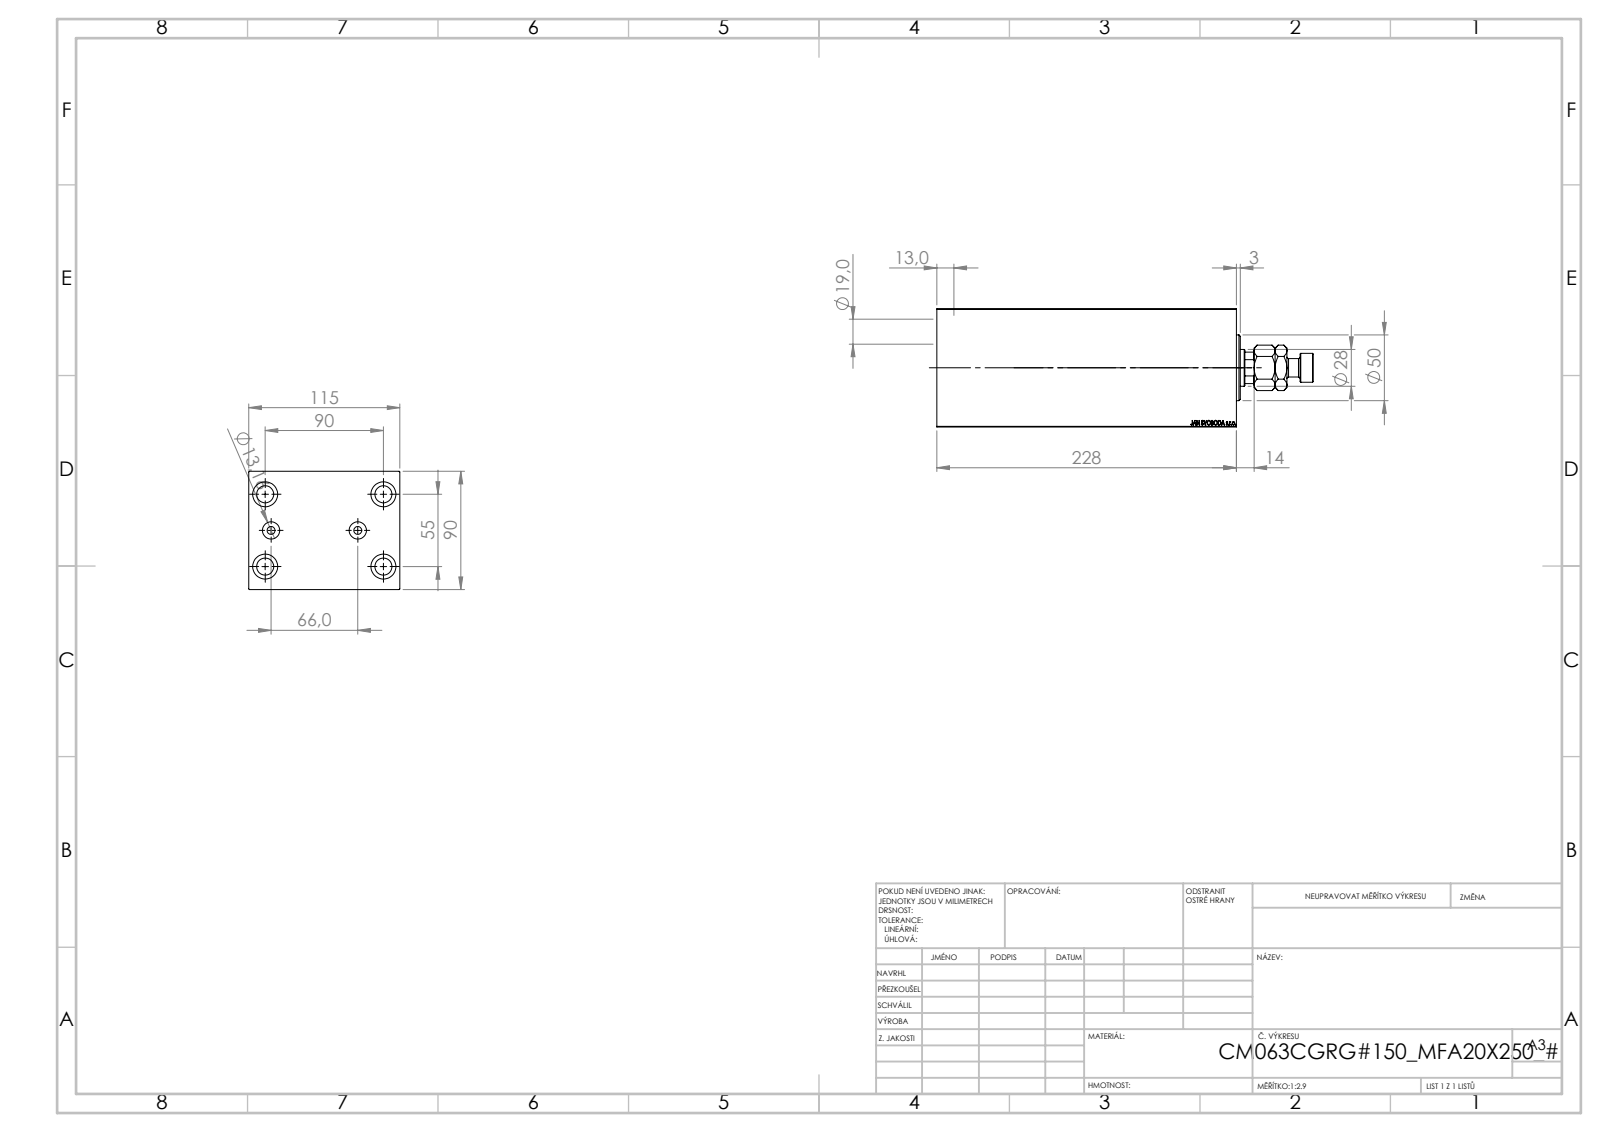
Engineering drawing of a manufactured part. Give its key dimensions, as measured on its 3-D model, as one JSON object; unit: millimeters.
{"part_name": "V450CM_C_VCP; MFA; V450CM_C_Body; V450CM_VC_B", "step_written_by": "SolidWorks 2019 (CONFIG_CONTROL_DESIGN)", "units": "millimeters", "bodies": {"solids": 4, "faces": 913, "planar": 425, "cylindrical": 62, "other": 426}, "overall_size": [286.5, 115, 90], "volume_mm3": 1864000, "surface_area_mm2": 235576, "round_holes": [[13, 4], [19, 4], [6, 2], [13.16, 2], [18.5, 1], [28, 1], [31.5, 1], [63, 1], [65, 1], [72, 1]], "round_bosses_or_shafts": [[50, 1], [22, 1], [14, 1]], "partial_cylinders_radius": [[13.5, 1]], "face_to_face_distances": [90, 115, 228, 48.5, 179.5, 218, 10, 5, 169.5, 19.5], "hole_center_spacings": [30, 52.74, 82.71, 33, 55, 90, 105.48, 66]}
